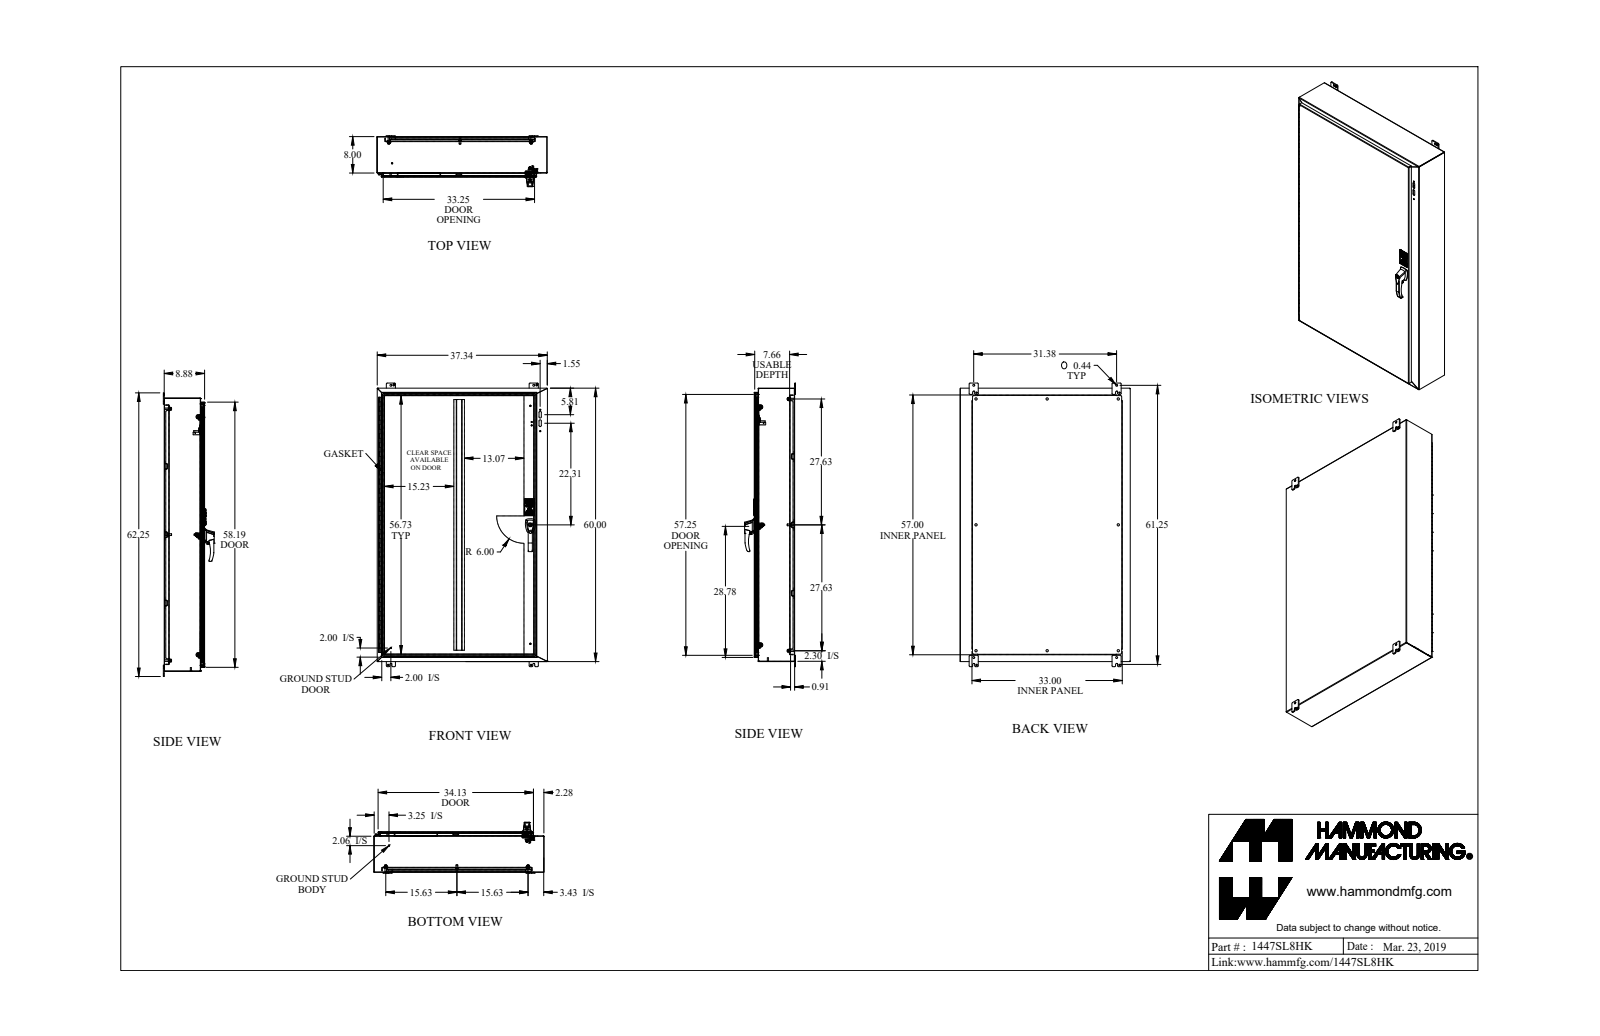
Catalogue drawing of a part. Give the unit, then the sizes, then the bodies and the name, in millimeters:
Units: millimetres
Overall size (bounding box): 1581.14 × 949.33 × 283.9
Round holes (diameter × count): ⌀12.7 ×8, ⌀4.47 ×6, ⌀7.94 ×6, ⌀7.81 ×4, ⌀11.11 ×4, ⌀11.3 ×4, ⌀6.35 ×3, ⌀6.73 ×3, ⌀10.49 ×3, ⌀3.97 ×2, ⌀4.39 ×2, ⌀4.98 ×2
Round bosses / shafts (diameter × count): ⌀9.53 ×13, ⌀6.35 ×9, ⌀16.51 ×8, ⌀8.38 ×8, ⌀25.4 ×7, ⌀3.97 ×6, ⌀16 ×2, ⌀12.95 ×2
Partial cylindrical surfaces — rounded edges, fillets, slot ends (radius × count): R4.76 ×35, R2 ×28, R6.35 ×21, R0.17 ×16, R2.93 ×16, R3.17 ×16, R0.76 ×10, R3.83 ×8
Main face-to-face distances: 1.83, 223.6, 221.77, 225.43, 2.41, 197.39, 195.56, 26.21, 28.04, 199.8
Hole centre spacings: 793.75, 796.93, 1458.39, 1714.16, 28.21, 396.88, 701.67, 766.9
Volume: 12 000 000 mm³ · Surface area: 12 050 000 mm²
Bodies: 69 solids, 1687 faces (1043 planar, 504 cylindrical, 140 other)
Part name (STEP PRODUCT): 1447SL8HK
STEP written by: SolidWorks 2019 (AUTOMOTIVE_DESIGN)
